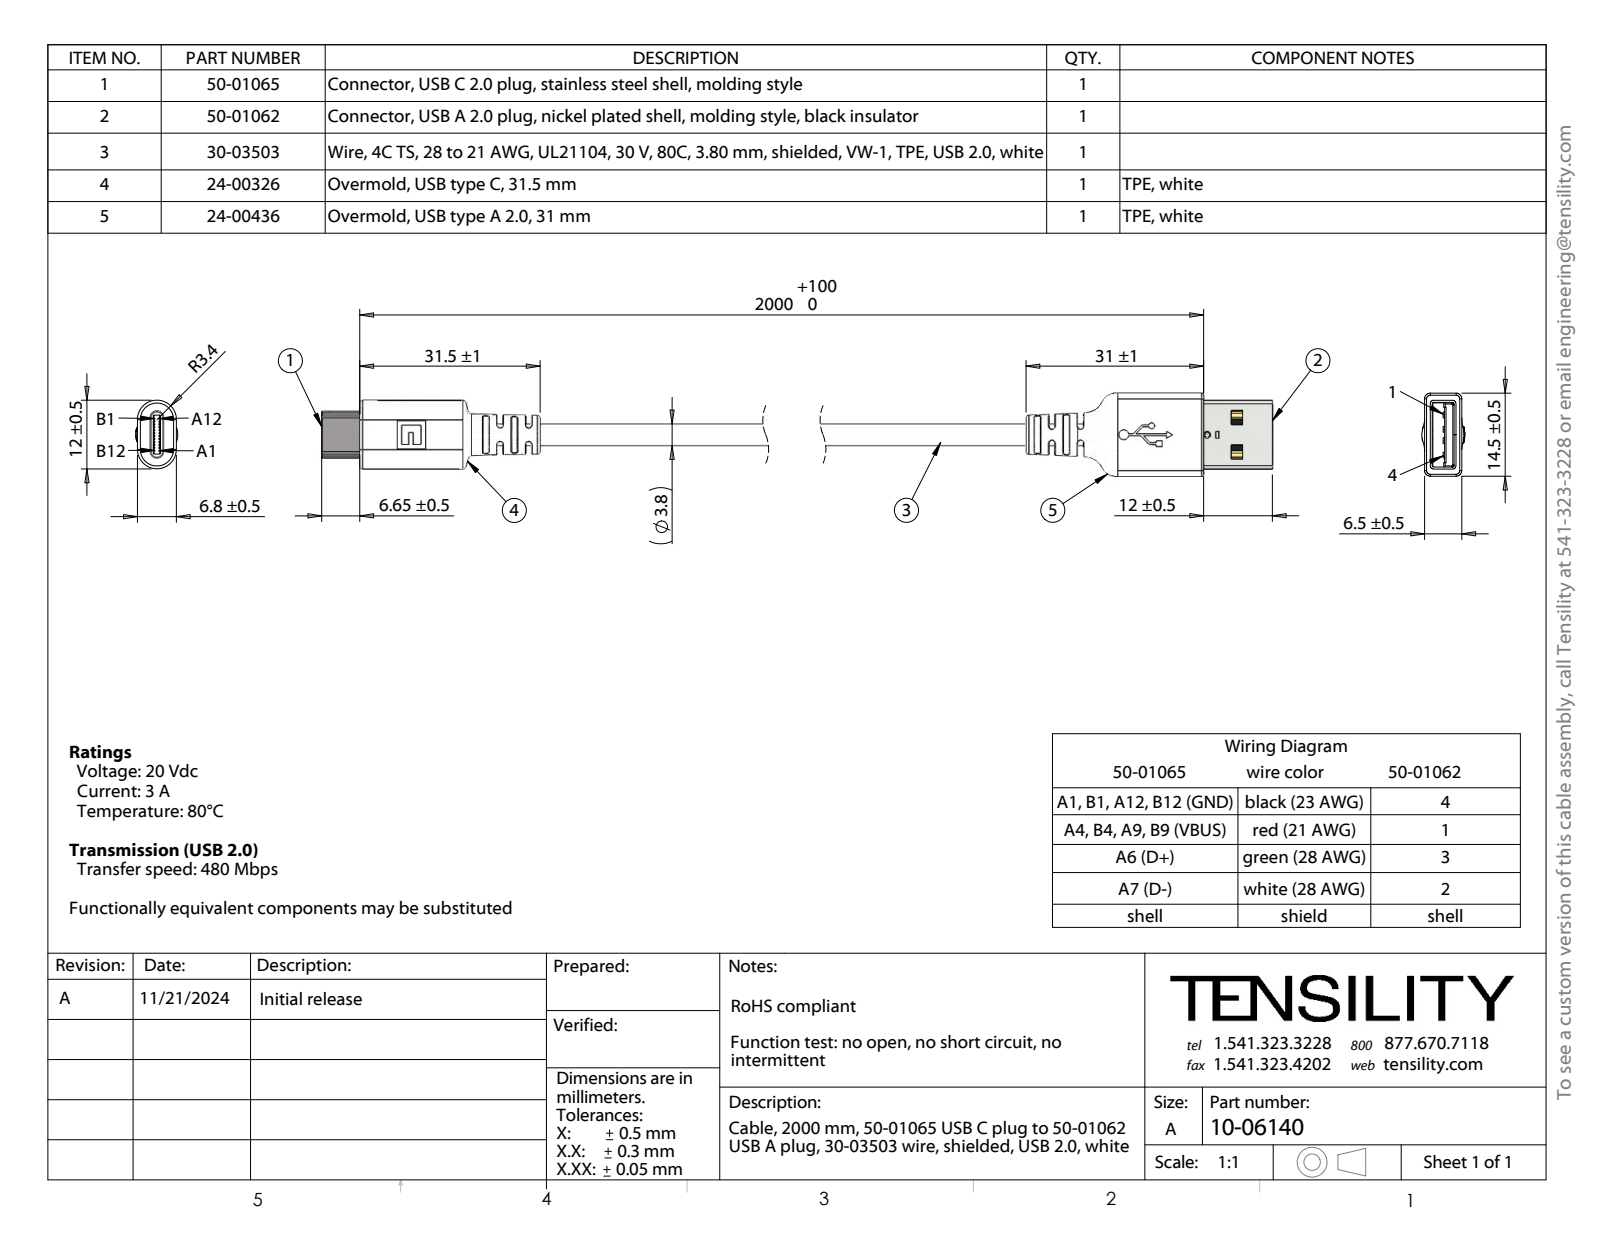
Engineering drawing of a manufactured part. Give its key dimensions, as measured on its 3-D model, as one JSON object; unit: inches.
{"part_name": "50-01062_pin2; 30-03503_blunt cut; 50-01062_pin1; 24-00436 (+8 more)", "step_written_by": "SolidWorks 2021 (CONFIG_CONTROL_DESIGN)", "units": "inches", "bodies": {"solids": 125, "faces": 1970, "planar": 1014, "cylindrical": 630, "other": 326}, "overall_size": [8.313, 0.571, 0.297], "volume_in3": 0.361, "surface_area_in2": 35, "round_holes": [[0.041, 1], [0.069, 1], [0.103, 1], [0.104, 1], [0.112, 1]], "round_bosses_or_shafts": [[0.033, 2], [0.15, 1], [0.104, 1], [0.047, 1], [0.039, 1]], "partial_cylinders_radius": [[0.01, 40], [0.008, 34], [0.02, 32], [0.014, 14], [0.016, 14], [0.012, 13], [0.012, 5], [0.024, 5]], "face_to_face_distances": [0.014, 0.163, 0.098, 0.177, 0.15, 0.049, 0.256, 0.053, 0.216, 0.202], "hole_center_spacings": [0.201]}
